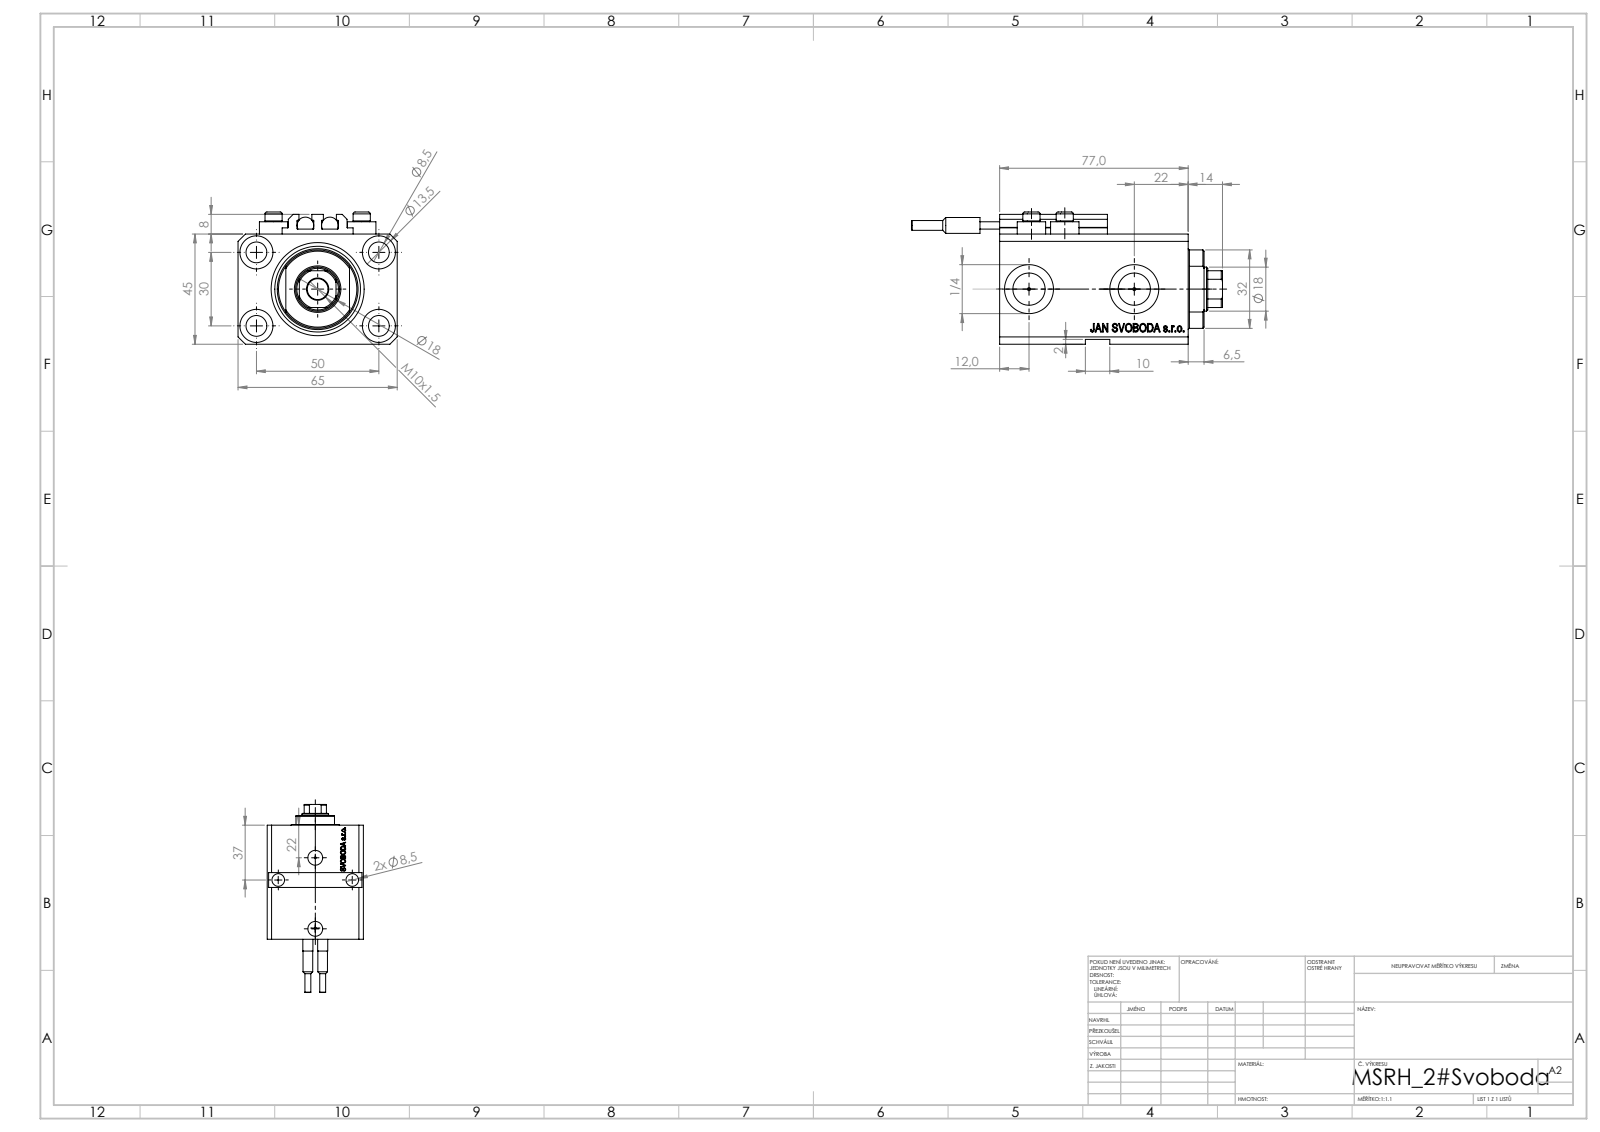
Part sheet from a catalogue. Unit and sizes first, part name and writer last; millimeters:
Units: millimetres
Overall size (bounding box): 127 × 65 × 54
Round holes (diameter × count): ⌀8.5 ×7, ⌀1.25 ×4, ⌀4 ×4, ⌀13.5 ×4, ⌀10 ×2, ⌀13.16 ×2, ⌀20 ×2, ⌀18 ×1, ⌀25 ×1, ⌀38 ×1
Round bosses / shafts (diameter × count): ⌀11.6 ×4, ⌀7 ×4, ⌀6.8 ×2, ⌀6.5 ×2, ⌀4 ×2
Partial cylindrical surfaces — rounded edges, fillets, slot ends (radius × count): R0.2 ×10, R8.5 ×1, R16 ×1
Main face-to-face distances: 45, 65, 63, 2, 14, 3, 77, 47, 5, 6.9
Hole centre spacings: 29.15, 50, 13.6, 15.12, 18.81, 18.97, 26.22, 26.61
Volume: 203 348 mm³ · Surface area: 61 935 mm²
Bodies: 10 solids, 1119 faces (543 planar, 138 cylindrical, 438 other)
Part name (STEP PRODUCT): V250CE_VC_E; ALLEN BOLT V250CE; V250CE_E_Body; SWITCH_V250CE (+1 more)
STEP written by: SolidWorks 2019 (CONFIG_CONTROL_DESIGN)
